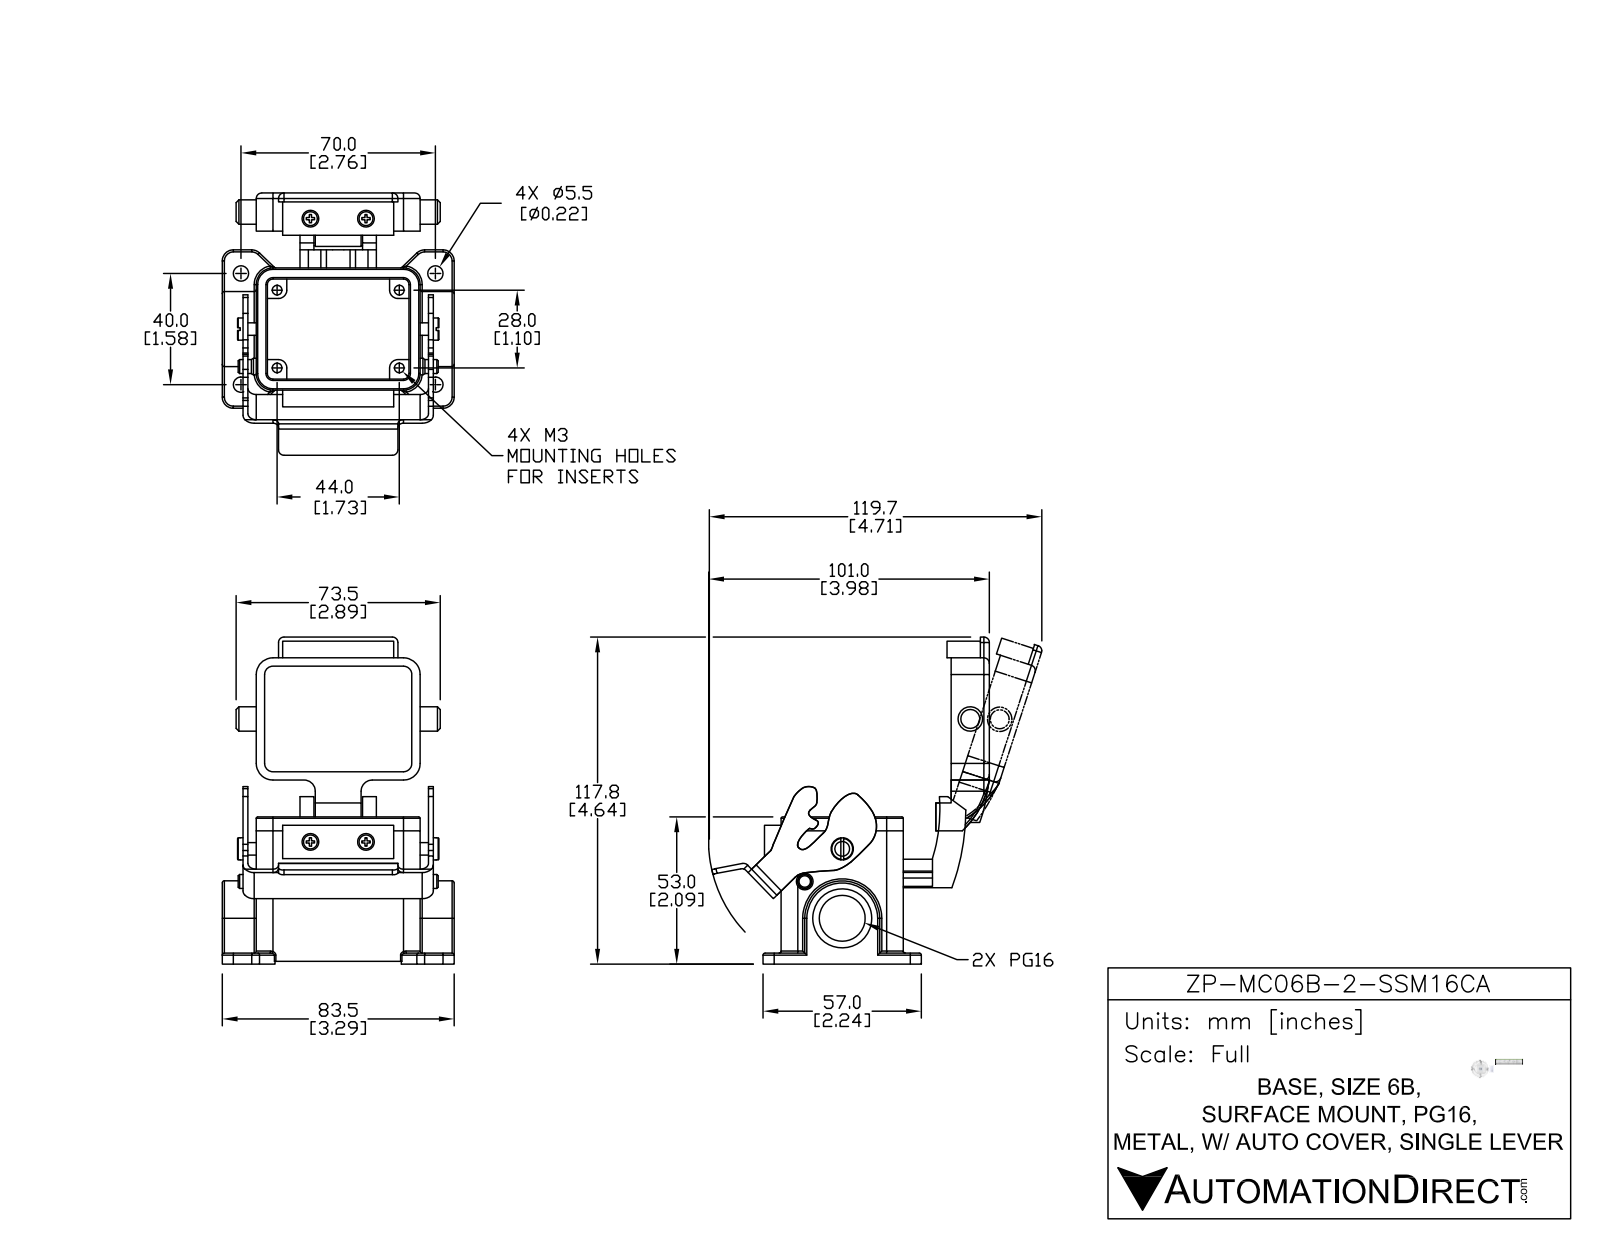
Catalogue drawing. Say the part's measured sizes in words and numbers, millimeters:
The part is named "ZP-MC06B-2-SSM16CA". Its 3-D file was written by "SolidWorks 2014 (AUTOMOTIVE_DESIGN)". It is 11 solids with 526 faces: 229 planar, 173 cylindrical and 124 other. Overall it measures 117.75 by 94.41 by 83.5 millimeters. Its volume is 95 292 cubic millimeters and its surface area 58 612 square millimeters. Round holes: 4 of diameter 3.5, 4 of diameter 5.5, 1 of diameter 4.5, 1 of diameter 5.32, 1 of diameter 16.5, 1 of diameter 21.25. Round bosses or shafts: 5 of diameter 5, 2 of diameter 8, 1 of diameter 8.8, 1 of diameter 6. Partial cylindrical surfaces (rounded edges, fillets, slot ends): 24 of radius 2, 22 of radius 0.75, 12 of radius 3, 12 of radius 4, 8 of radius 0.5, 8 of radius 6, 1 of radius 4.25, 1 of radius 13.5. The main face-to-face distances are 4, 3, 1.75, 40, 1, 44, 48, 5, 70.98, 7.5. The hole center spacings are 14.53, 35.93, 57.37, 66.12, 27, 40, 44, 51.62.
